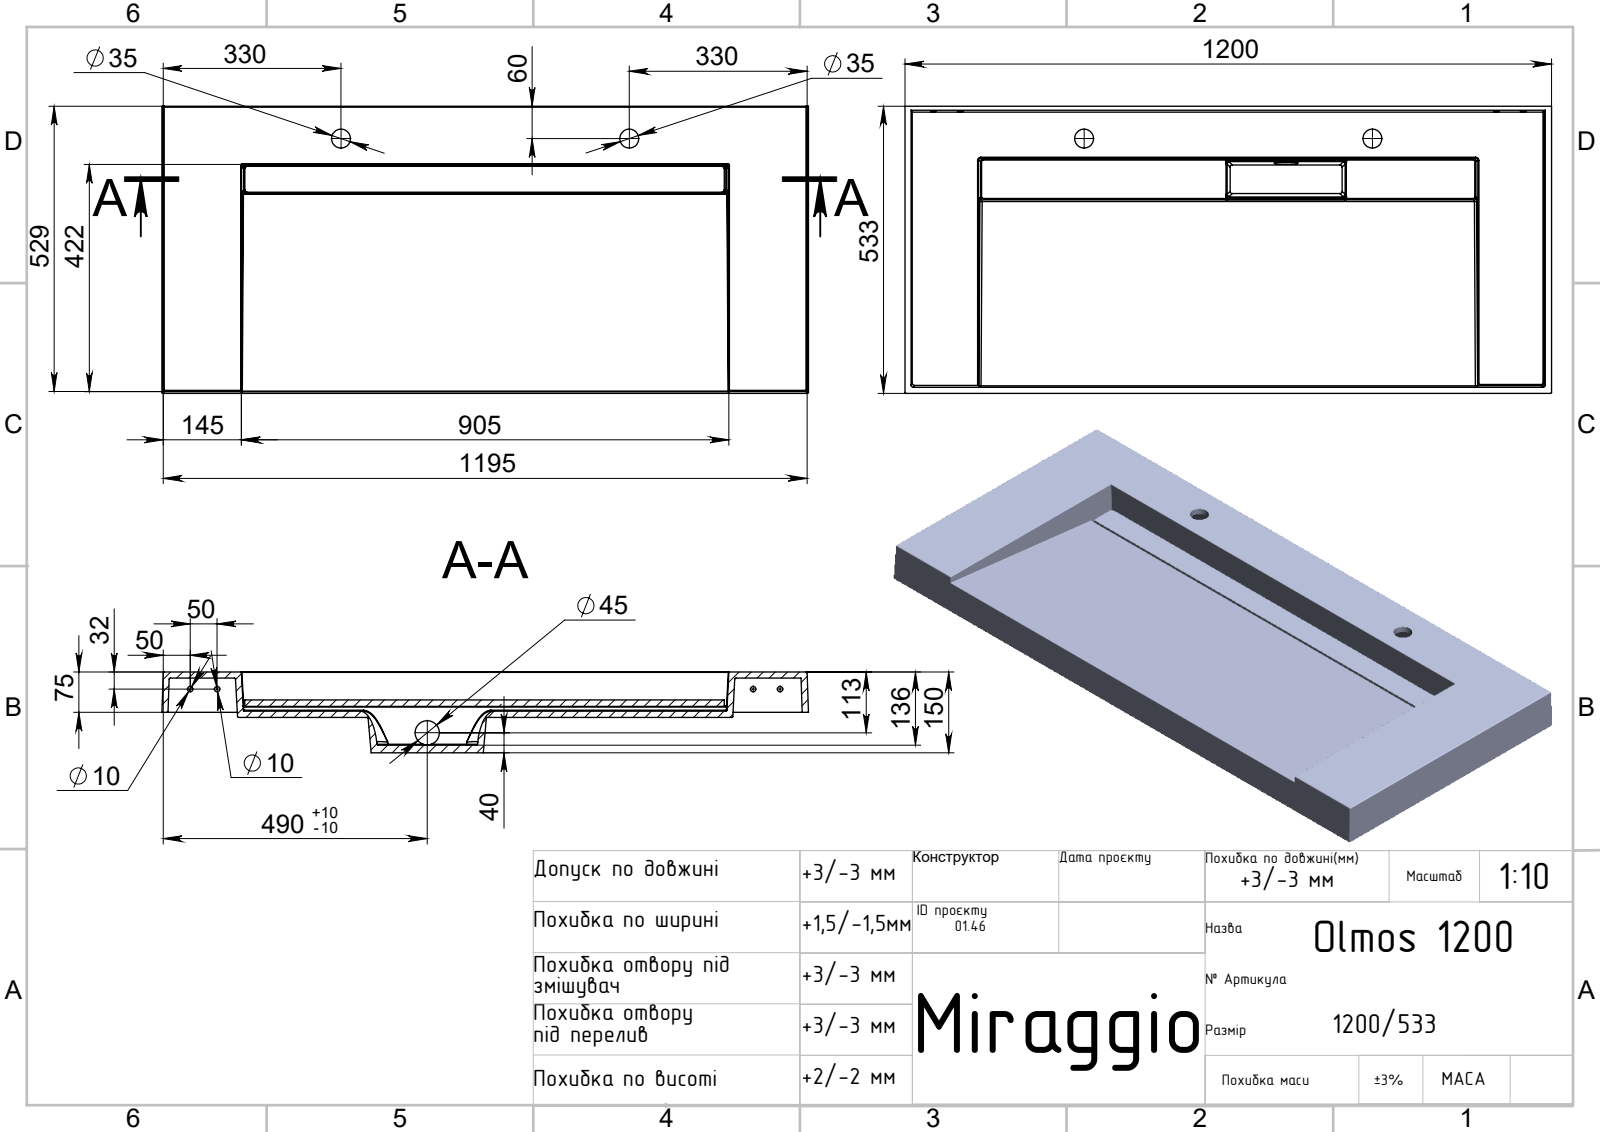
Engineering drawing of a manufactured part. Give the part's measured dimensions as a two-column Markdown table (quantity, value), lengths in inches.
| quantity | value |
| --- | --- |
| part name | Olmos 1200 |
| STEP written by | SolidWorks 2020 (AUTOMOTIVE_DESIGN) |
| units | inches |
| bodies | 1 solid, 217 faces (47 planar, 99 cylindrical, 71 other) |
| overall size | 47.254 × 20.978 × 5.906 |
| volume | 712.1 in³ |
| surface area | 3 240 in² |
| round holes (diameter × count) | 0.394 × 4, 1.378 × 2, 1.772 × 1 |
| partial cylindrical surfaces (radius × count) | 0.079 × 37, 0.039 × 23, 0.157 × 13, 0.197 × 4, 0.827 × 4 |
| main face-to-face distances | 0.453, 2.874, 0.452, 0.453, 3.327, 2.953, 2.52, 0.807, 2.067, 1.28 |
| hole center spacings | 1.969, 41.142, 15.682, 17.614, 21.069, 24.031, 25.984, 39.173 |
